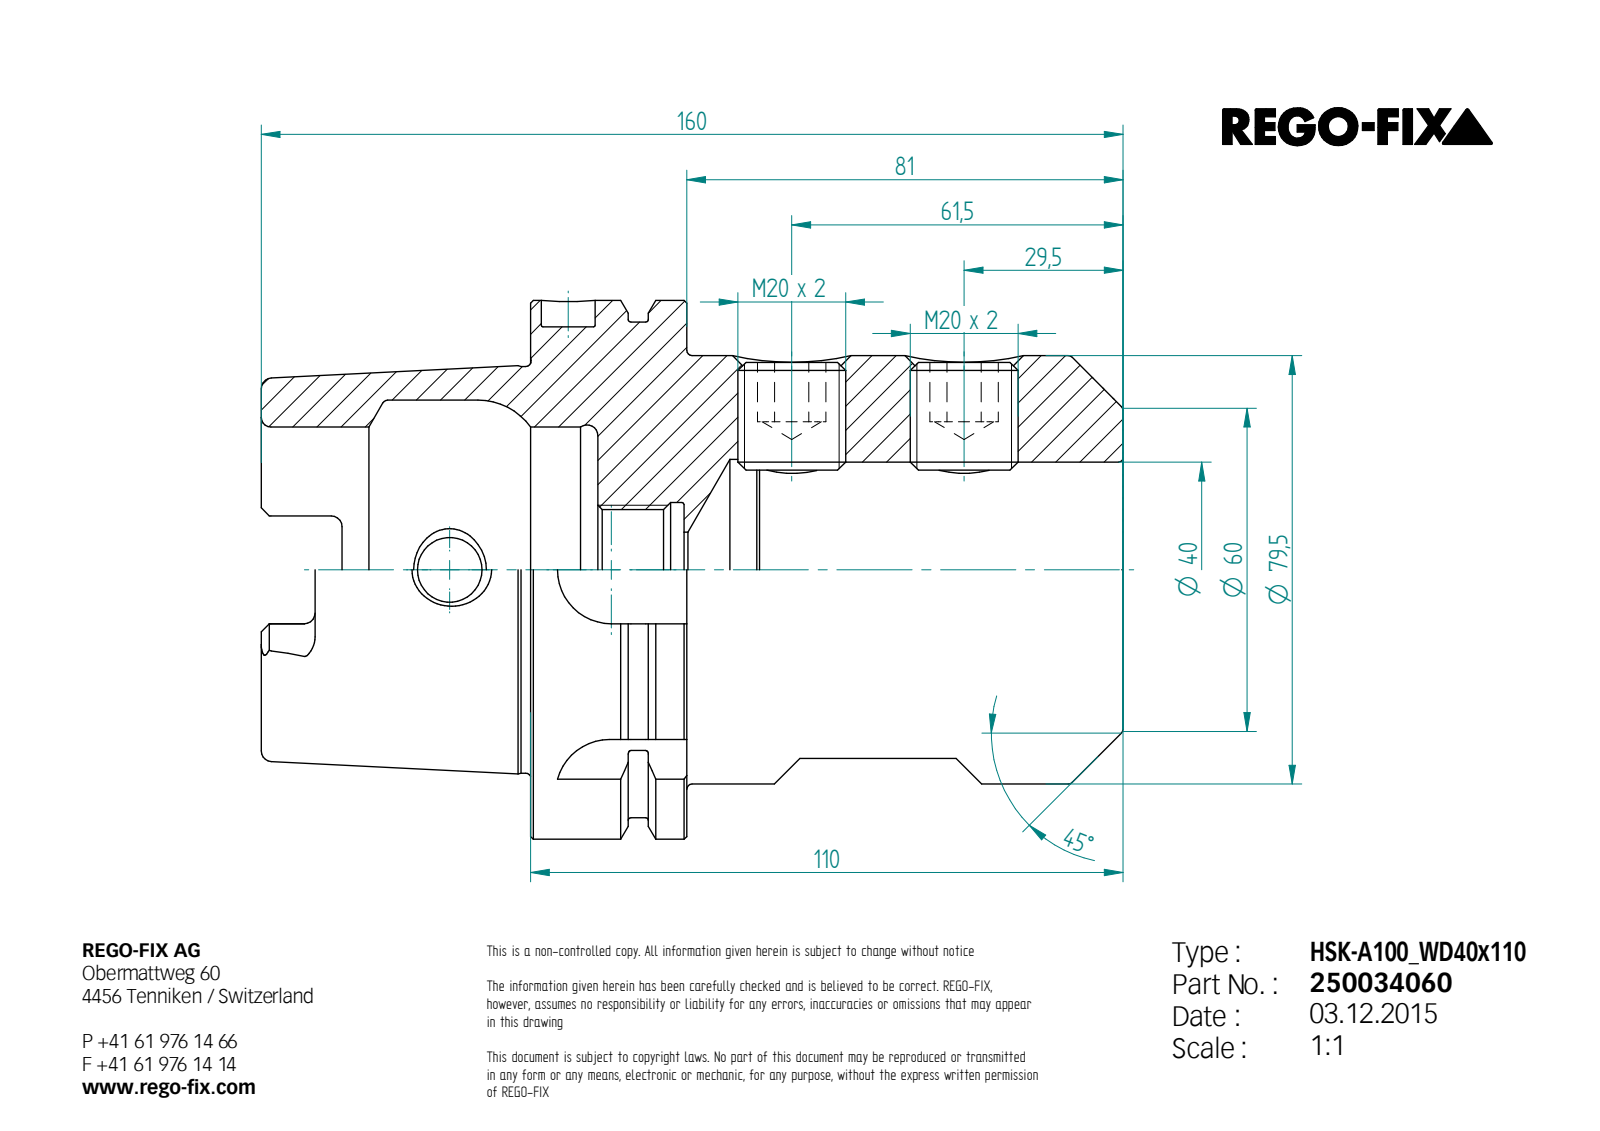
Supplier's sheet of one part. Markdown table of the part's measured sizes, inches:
| quantity | value |
| --- | --- |
| STEP written by | Unknown (AUTOMOTIVE_DESIGN) |
| units | inches |
| bodies | 3 solids, 164 faces (66 planar, 38 cylindrical, 60 other) |
| overall size | 6.299 × 3.937 × 3.937 |
| volume | 33.19 in³ |
| surface area | 128.4 in² |
| round holes (diameter × count) | 0.702 × 2, 0.335 × 1, 0.394 × 1, 0.472 × 1, 0.551 × 1, 0.881 × 1, 0.984 × 1, 1.575 × 1, 1.614 × 1, 2.087 × 1, 2.48 × 1 |
| round bosses / shafts (diameter × count) | 0.787 × 2, 3.937 × 1, 3.622 × 1, 3.13 × 1, 2.971 × 1 |
| partial cylindrical surfaces (radius × count) | 0.079 × 6, 0.192 × 4, 0.394 × 2, 0.433 × 1 |
| main face-to-face distances | 1.142, 0.492, 0.65, 4.331, 3.839, 3.189, 1.969, 2.461, 3.11, 6.299 |
| hole center spacings | 1.26, 1.634, 2.894 |
